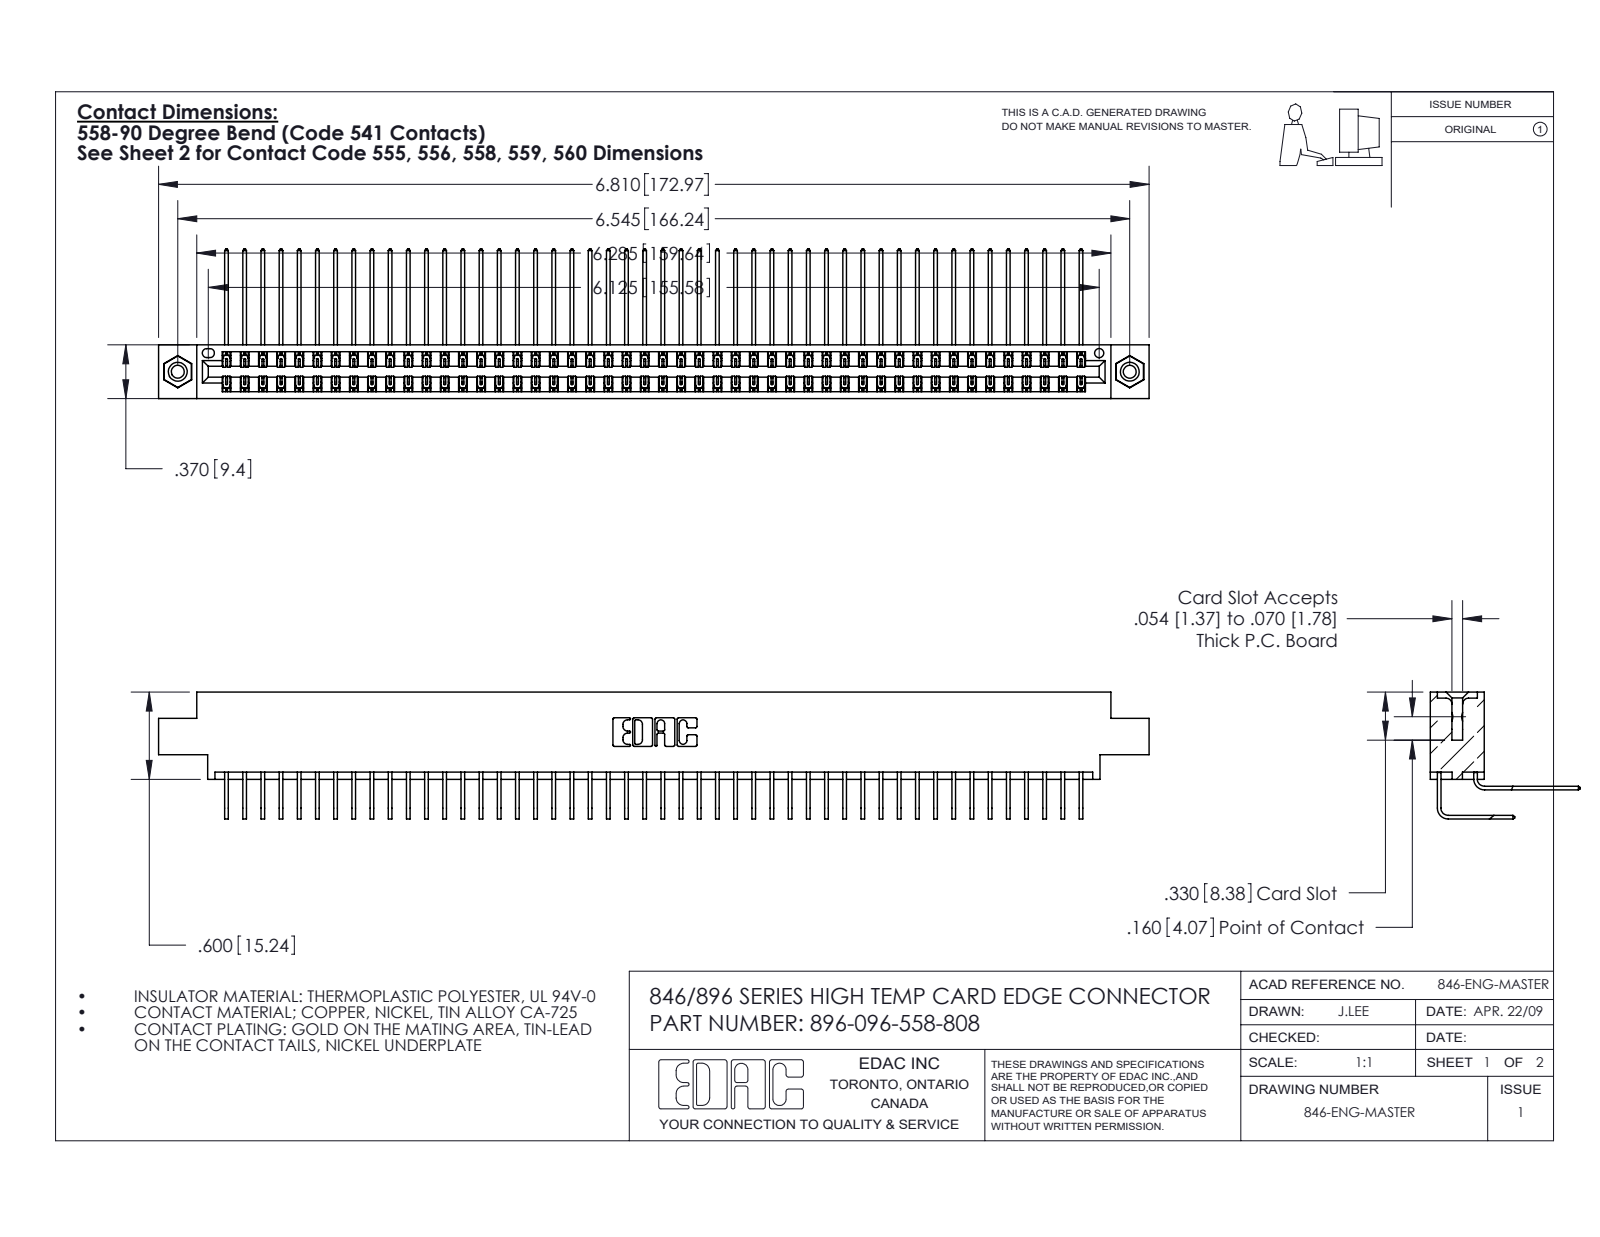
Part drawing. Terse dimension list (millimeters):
name: 345-292-001_558 559 Tail - 1; 345-292-001_558 Tail - 2; 345-250-001_345-250-003-102; 396-096-558-808 (+1 more)
written by: SolidWorks 2016 (CONFIG_CONTROL_DESIGN)
unit: mm
bodies: 99 solids, 5370 faces (3664 planar, 1690 cylindrical, 16 other)
size: 173 × 26.2 × 22.2
volume: 17 300 mm³; area: 26 740 mm²
holes: 2× ⌀2.3, 2× ⌀3.2, 2× ⌀4, 1× ⌀1.6
bosses: 2× ⌀3.9
rounds: 144× R0.2, 22× R0.3, 6× R0.2, 6× R0.8, 3× R0.7, 2× R0.4, 2× R0.6, 2× R0.6
face distances: 8.2, 1.2, 0.6, 9.4, 6.4, 7.6, 1.8, 7, 5.6, 3.8
hole spacings: 6.2, 160.9, 166.2
